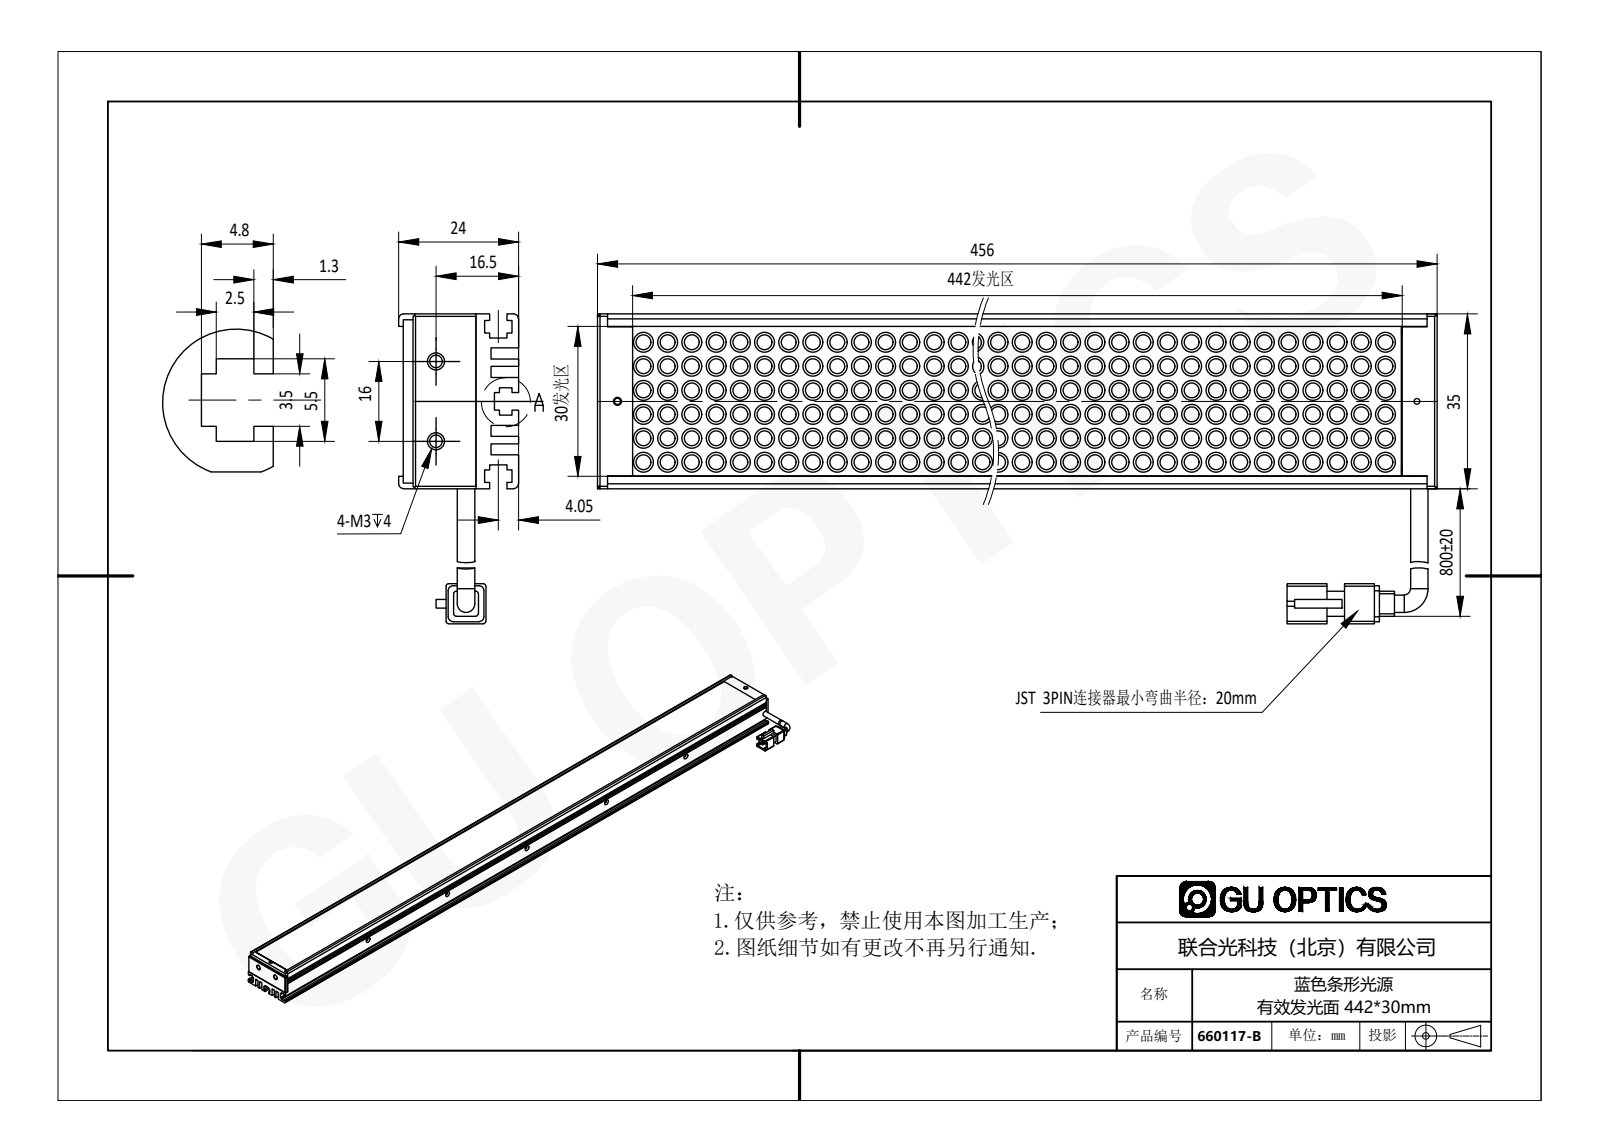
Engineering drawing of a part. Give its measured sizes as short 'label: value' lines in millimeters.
name: 660117-B
written by: SolidWorks 2016 (AUTOMOTIVE_DESIGN)
unit: mm
bodies: 8 solids, 3753 faces (813 planar, 2279 cylindrical, 661 other)
size: 456 × 62 × 24
volume: 198 847 mm³; area: 229 218 mm²
holes: 5× ⌀1.6, 5× ⌀1.7, 2× ⌀1.5, 2× ⌀2.5, 2× ⌀2.8, 2× ⌀3, 1× ⌀1.1, 1× ⌀1.25, 1× ⌀2
bosses: 546× ⌀4, 546× ⌀3, 2× ⌀3.5
rounds: 12× R1, 8× R0.5, 1× R1.65
face distances: 2, 2.2, 8.6, 1, 2.5, 4, 9, 10.6, 10.8, 12.6
hole spacings: 75, 150, 448, 7, 74.02, 74.2, 149.01, 149.1
